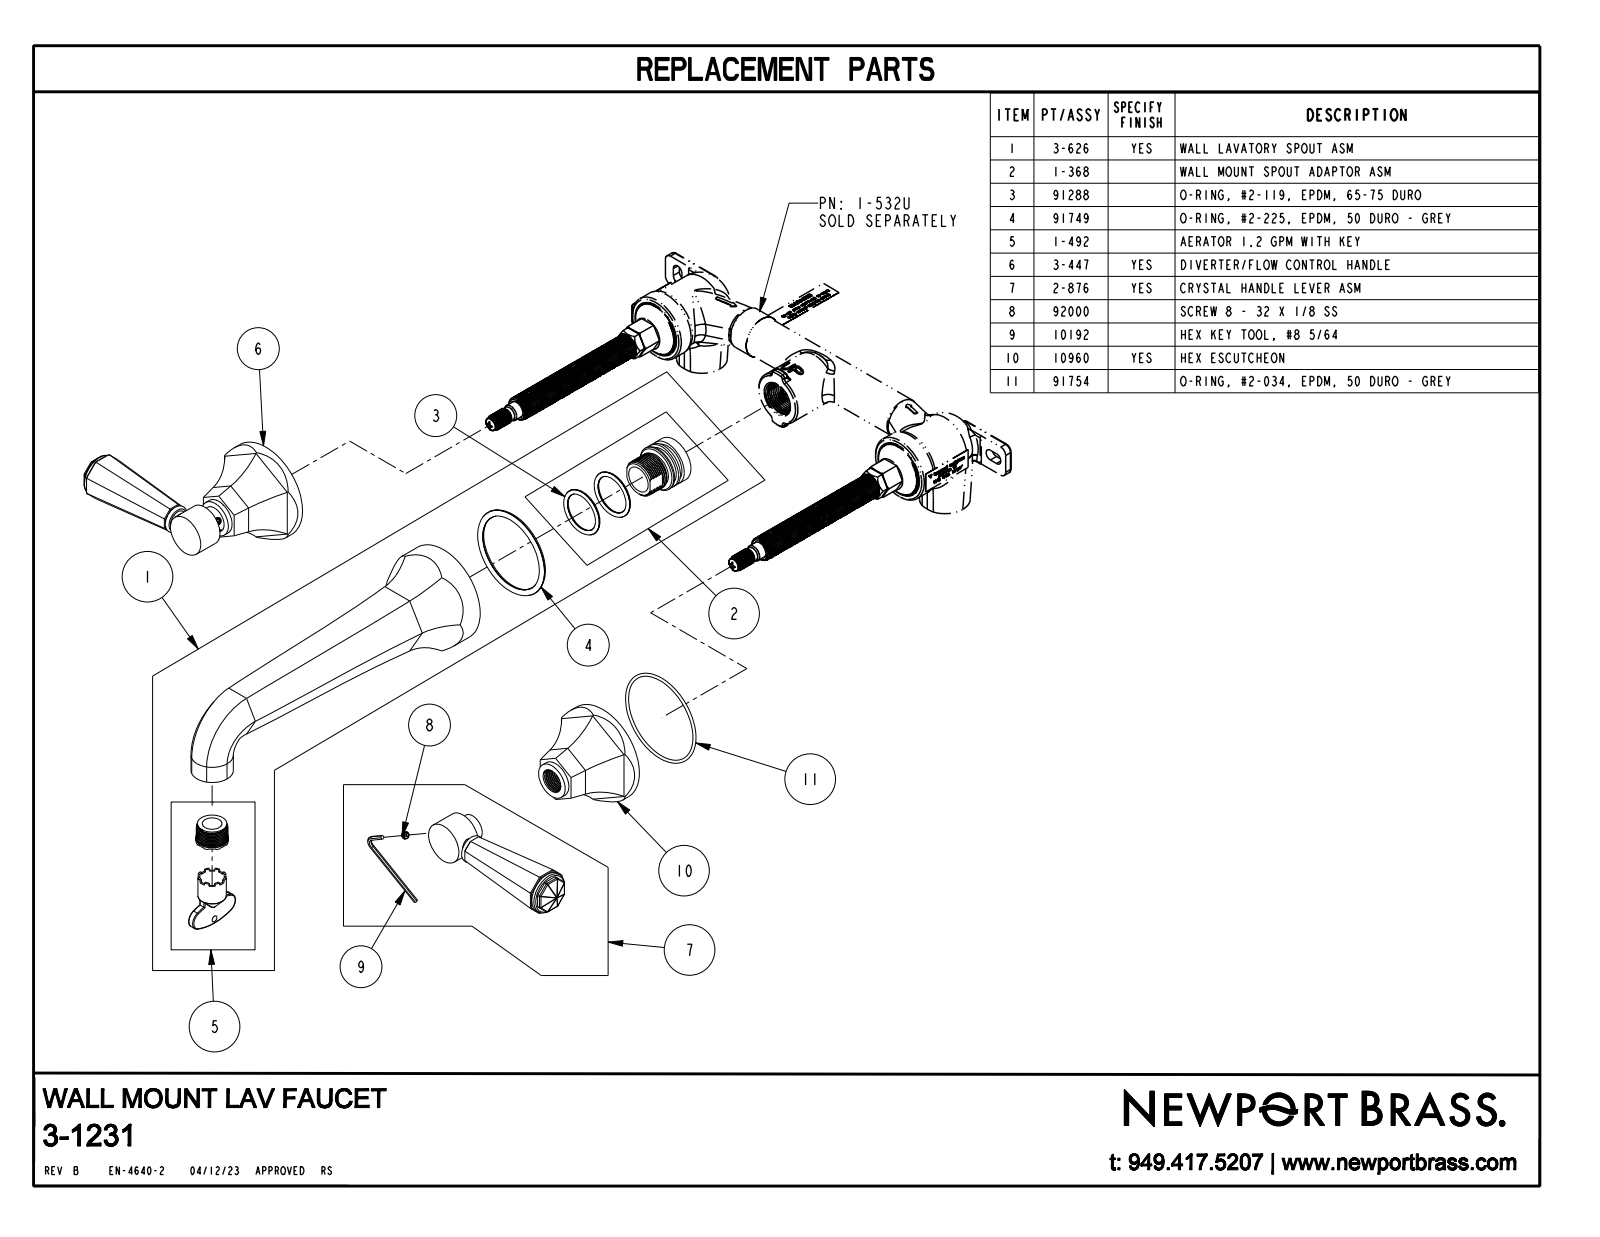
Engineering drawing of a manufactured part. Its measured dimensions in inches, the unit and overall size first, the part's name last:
Units: inches
Overall size (bounding box): 14.59 × 7.985 × 2.438
Round holes (diameter × count): ⌀0.385 ×1
Round bosses / shafts (diameter × count): ⌀2.375 ×3, ⌀0.98 ×3, ⌀0.86 ×2, ⌀0.625 ×2, ⌀0.365 ×1
Partial cylindrical surfaces — rounded edges, fillets, slot ends (radius × count): R0.03 ×40, R1.541 ×12
Main face-to-face distances: 0.157, 0.158, 0.159, 3.866, 1.977, 2.748, 1.527, 0.45, 1.647, 0.12
Volume: 23.4 in³ · Surface area: 95.49 in²
Bodies: 3 solids, 298 faces (140 planar, 90 cylindrical, 68 other)
Part name (STEP PRODUCT): 3-1231_SW0001
STEP written by: CREO PARAMETRIC BY PTC INC, 2018400 (AUTOMOTIVE_DESIGN)
